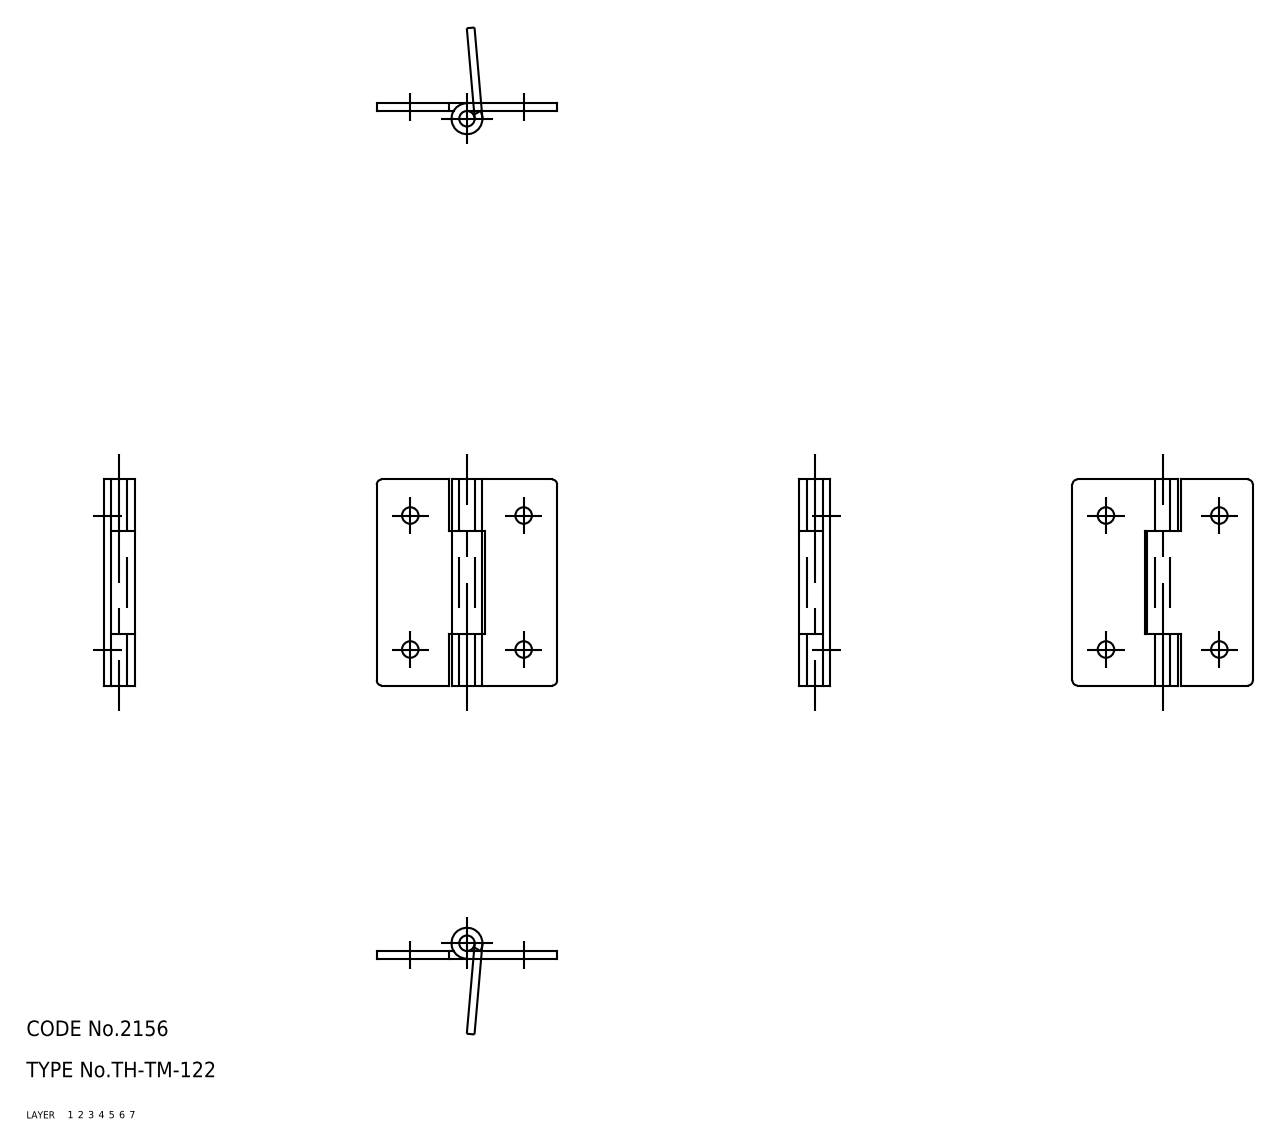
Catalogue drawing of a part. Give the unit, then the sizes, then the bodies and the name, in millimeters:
Units: millimetres
Overall size (bounding box): 40 × 35 × 6
Volume: 2 828 mm³ · Surface area: 4 303 mm²
Bodies: 3 solids, 42 faces (0 planar, 0 cylindrical, 42 other)
Part name (STEP PRODUCT): hinge piece_B; hinge piece_A; shaft; TH_TM_122_21445_36
STEP written by: CADfix (AUTOMOTIVE_DESIGN)
